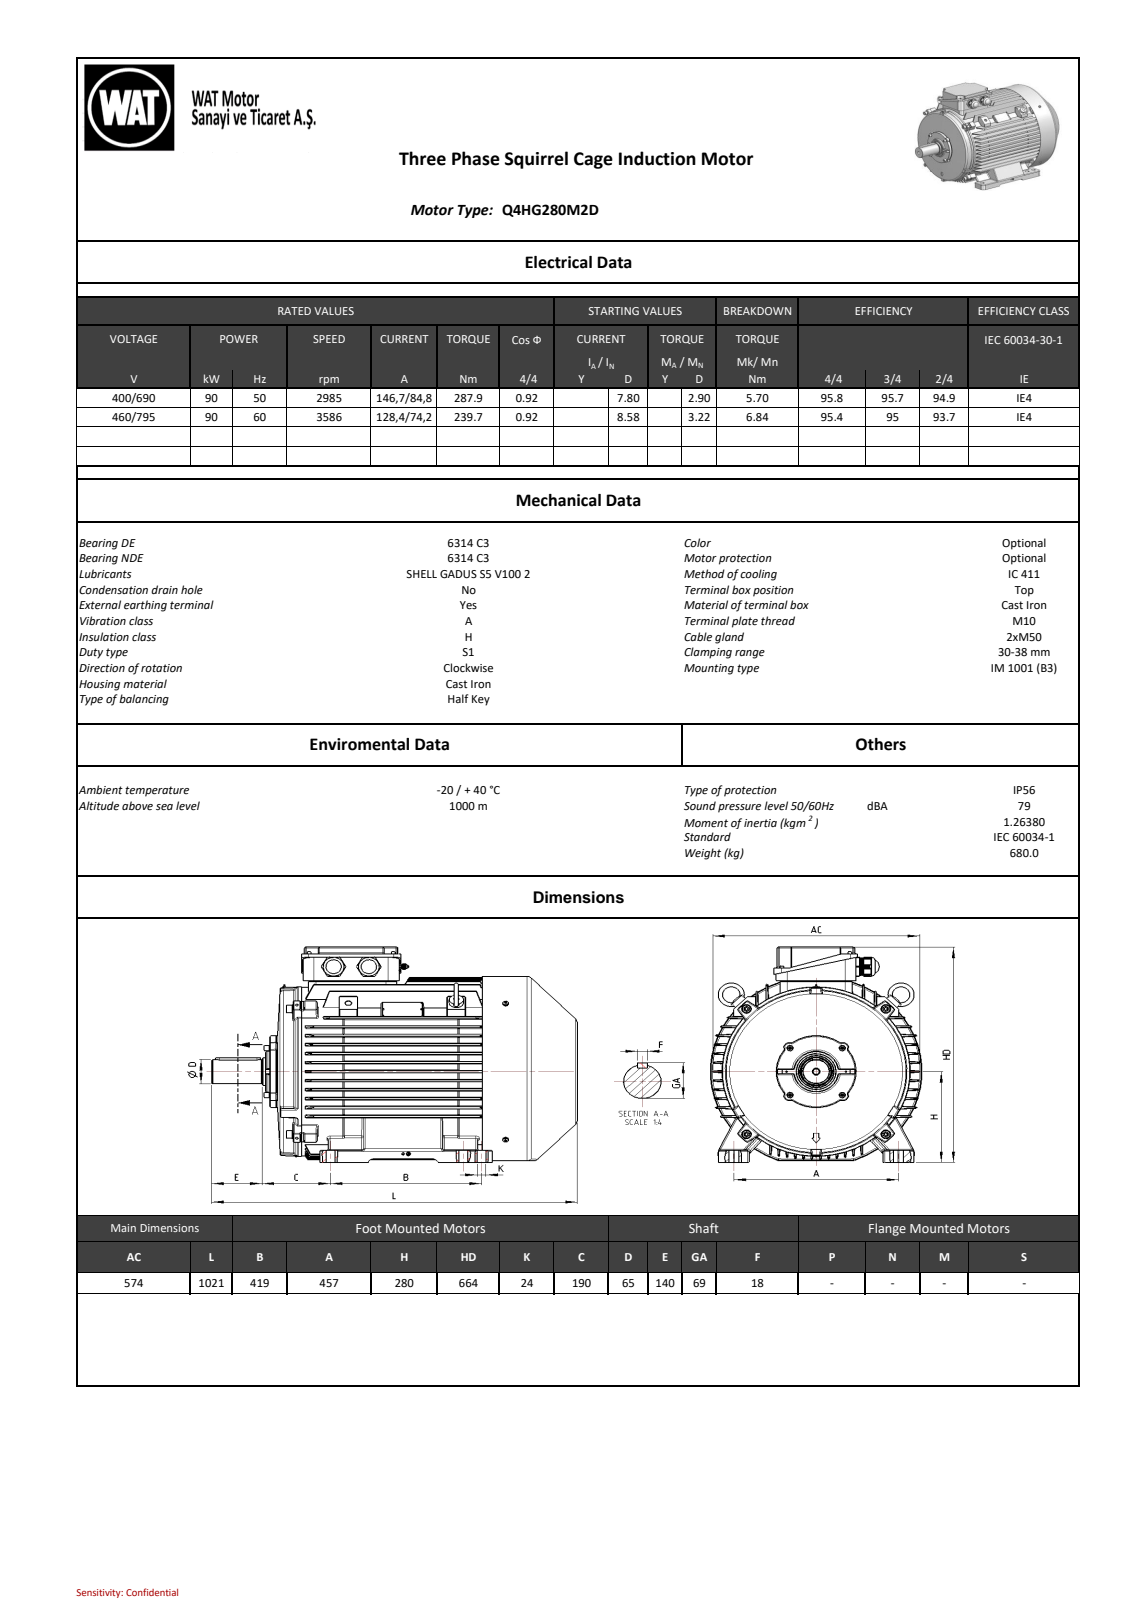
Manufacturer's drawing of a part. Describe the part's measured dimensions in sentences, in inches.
The part is named "AB_objects". Its 3-D file was written by "SIEMENS PLM Software NX2206.8101 (AUTOMOTIVE_DESIGN)". It is 0 solids with 4222 faces: 1798 planar, 1096 cylindrical and 1328 other. Overall it measures 40.193 by 26.15 by 23.15 inches. Round holes: 5 of diameter 0.283, 4 of diameter 0.581, 2 of diameter 0.177, 2 of diameter 0.728, 1 of diameter 0.394, 1 of diameter 0.472, 1 of diameter 0.827, 1 of diameter 23.031. Round bosses or shafts: 4 of diameter 1.079, 4 of diameter 0.932, 4 of diameter 0.63, 4 of diameter 0.619, 4 of diameter 0.394, 3 of diameter 0.713, 2 of diameter 2.283, 2 of diameter 2.169. Partial cylindrical surfaces (rounded edges, fillets, slot ends): 289 of radius 0.059, 77 of radius 0.079, 58 of radius 0.118, 54 of radius 0.039, 42 of radius 0.197, 25 of radius 0.157, 16 of radius 0.315, 13 of radius 0.008. The main face-to-face distances are 1.087, 2.175, 2.196, 1.241, 8.732, 0.531, 1.098, 1.098, 3.262, 1.085. The hole center spacings are 8.979, 10.767, 12.944, 15.228, 2.854, 21.535, 5.709.
